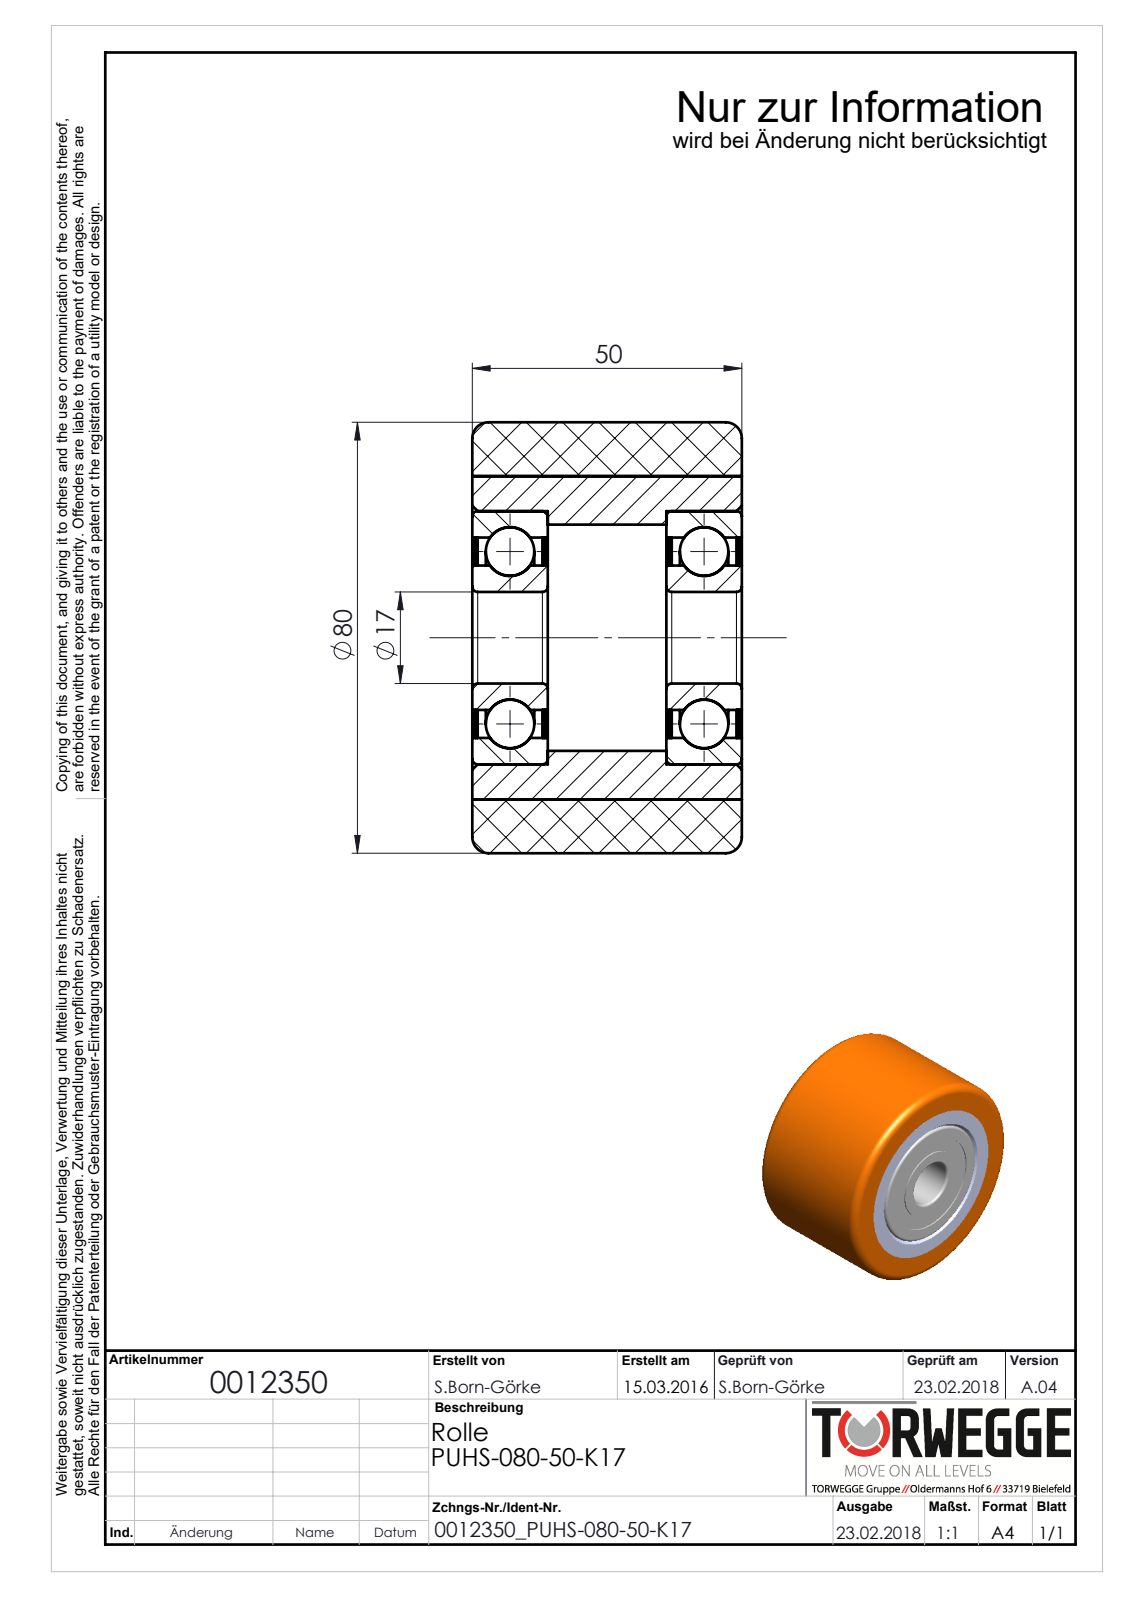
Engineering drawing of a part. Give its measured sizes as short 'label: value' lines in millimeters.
name: 0012350_PUHS-080-50-K17
written by: SolidWorks 2016 (AUTOMOTIVE_DESIGN)
unit: mm
bodies: 12 solids, 118 faces (22 planar, 52 cylindrical, 44 other)
size: 80 × 80 × 50
volume: 208 128 mm³; area: 70 571 mm²
holes: 1× ⌀17, 1× ⌀26.8, 1× ⌀37.2, 1× ⌀42, 1× ⌀47, 1× ⌀60
bosses: 1× ⌀80
face distances: 36, 0.5, 50, 13, 14, 1, 13.5, 36.5, 12.5, 35.5
